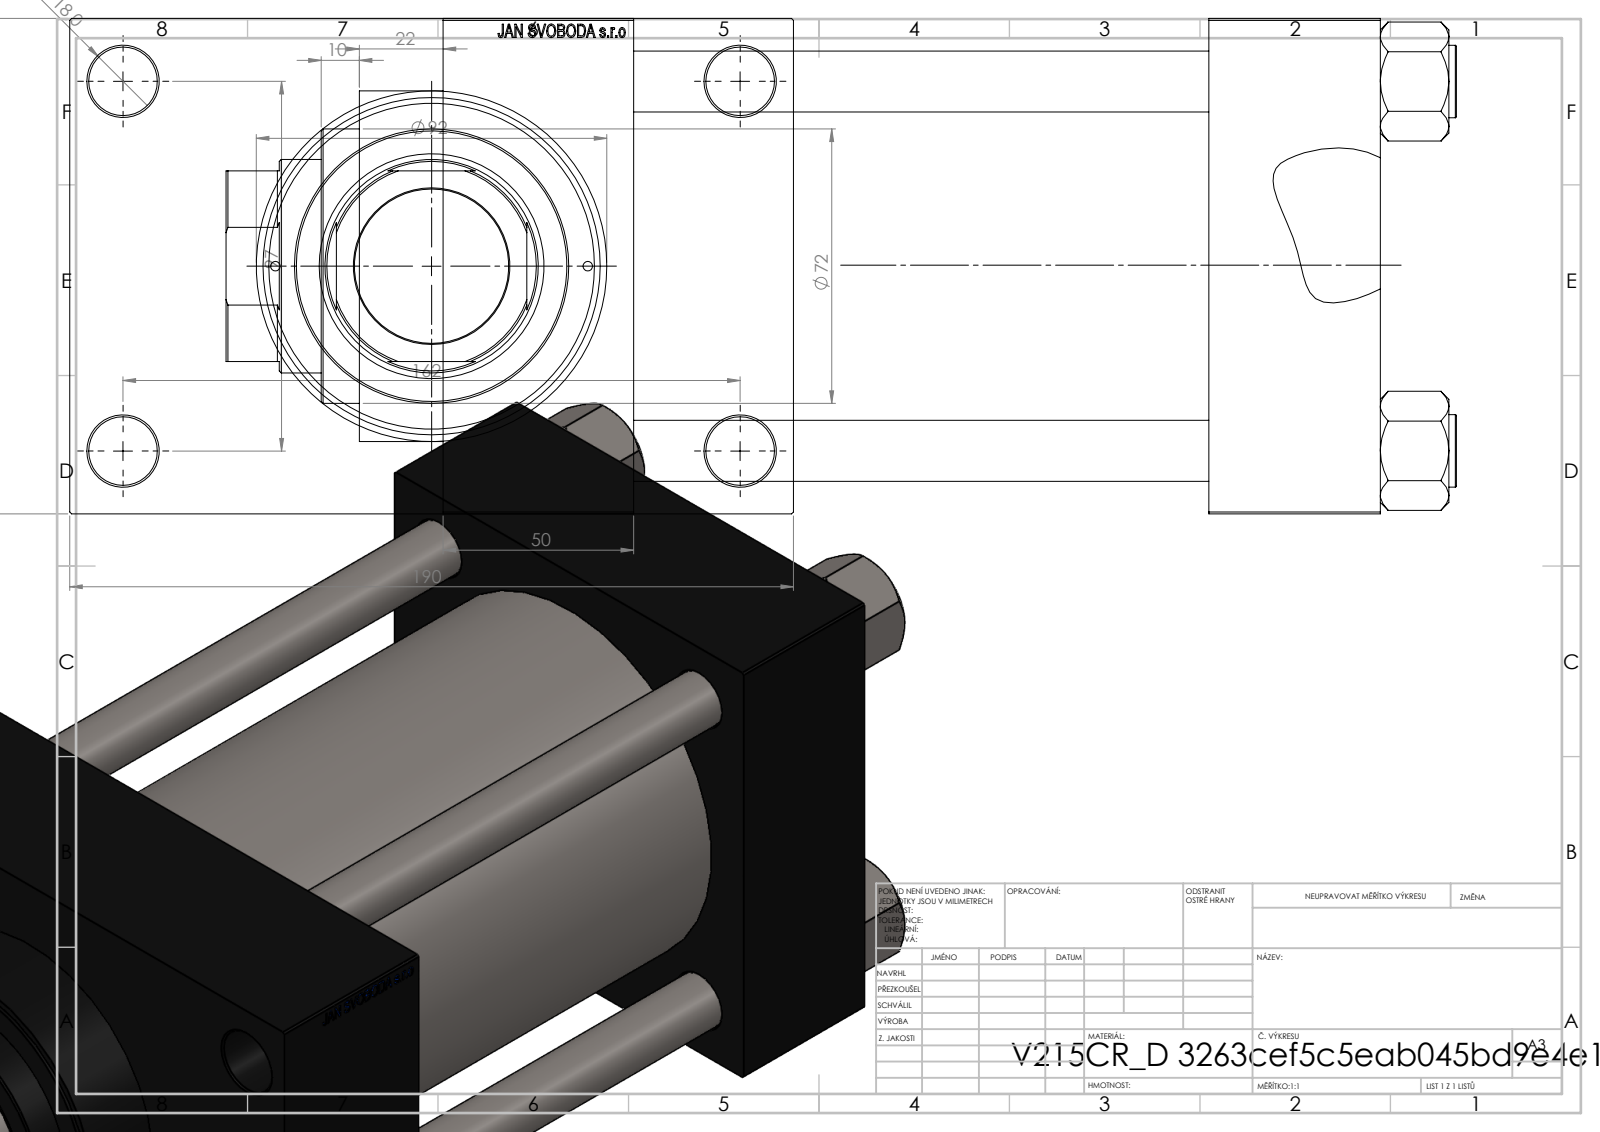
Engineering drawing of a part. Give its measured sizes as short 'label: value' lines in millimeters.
name: V215CR_D_TYCINKA; V215CR_D_Body; V215_VC_A; V215CR_VCP_D (+1 more)
written by: SolidWorks 2019 (CONFIG_CONTROL_DESIGN)
unit: mm
bodies: 11 solids, 1160 faces (547 planar, 93 cylindrical, 520 other)
size: 323 × 190 × 130
volume: 2 983 000 mm³; area: 441 652 mm²
holes: 4× ⌀16, 4× ⌀18, 2× ⌀2.5, 2× ⌀7, 2× ⌀26.44, 2× ⌀35, 1× ⌀40.5, 1× ⌀56, 1× ⌀59, 1× ⌀76, 1× ⌀85.5, 1× ⌀100
bosses: 4× ⌀19, 1× ⌀106, 1× ⌀92, 1× ⌀72
rounds: 1× R27
face distances: 130, 50, 45, 196, 151, 246, 201, 30, 160, 190
hole spacings: 32.55, 49.02, 62.87, 68.52, 94.41, 96.9, 101.73, 102.27
